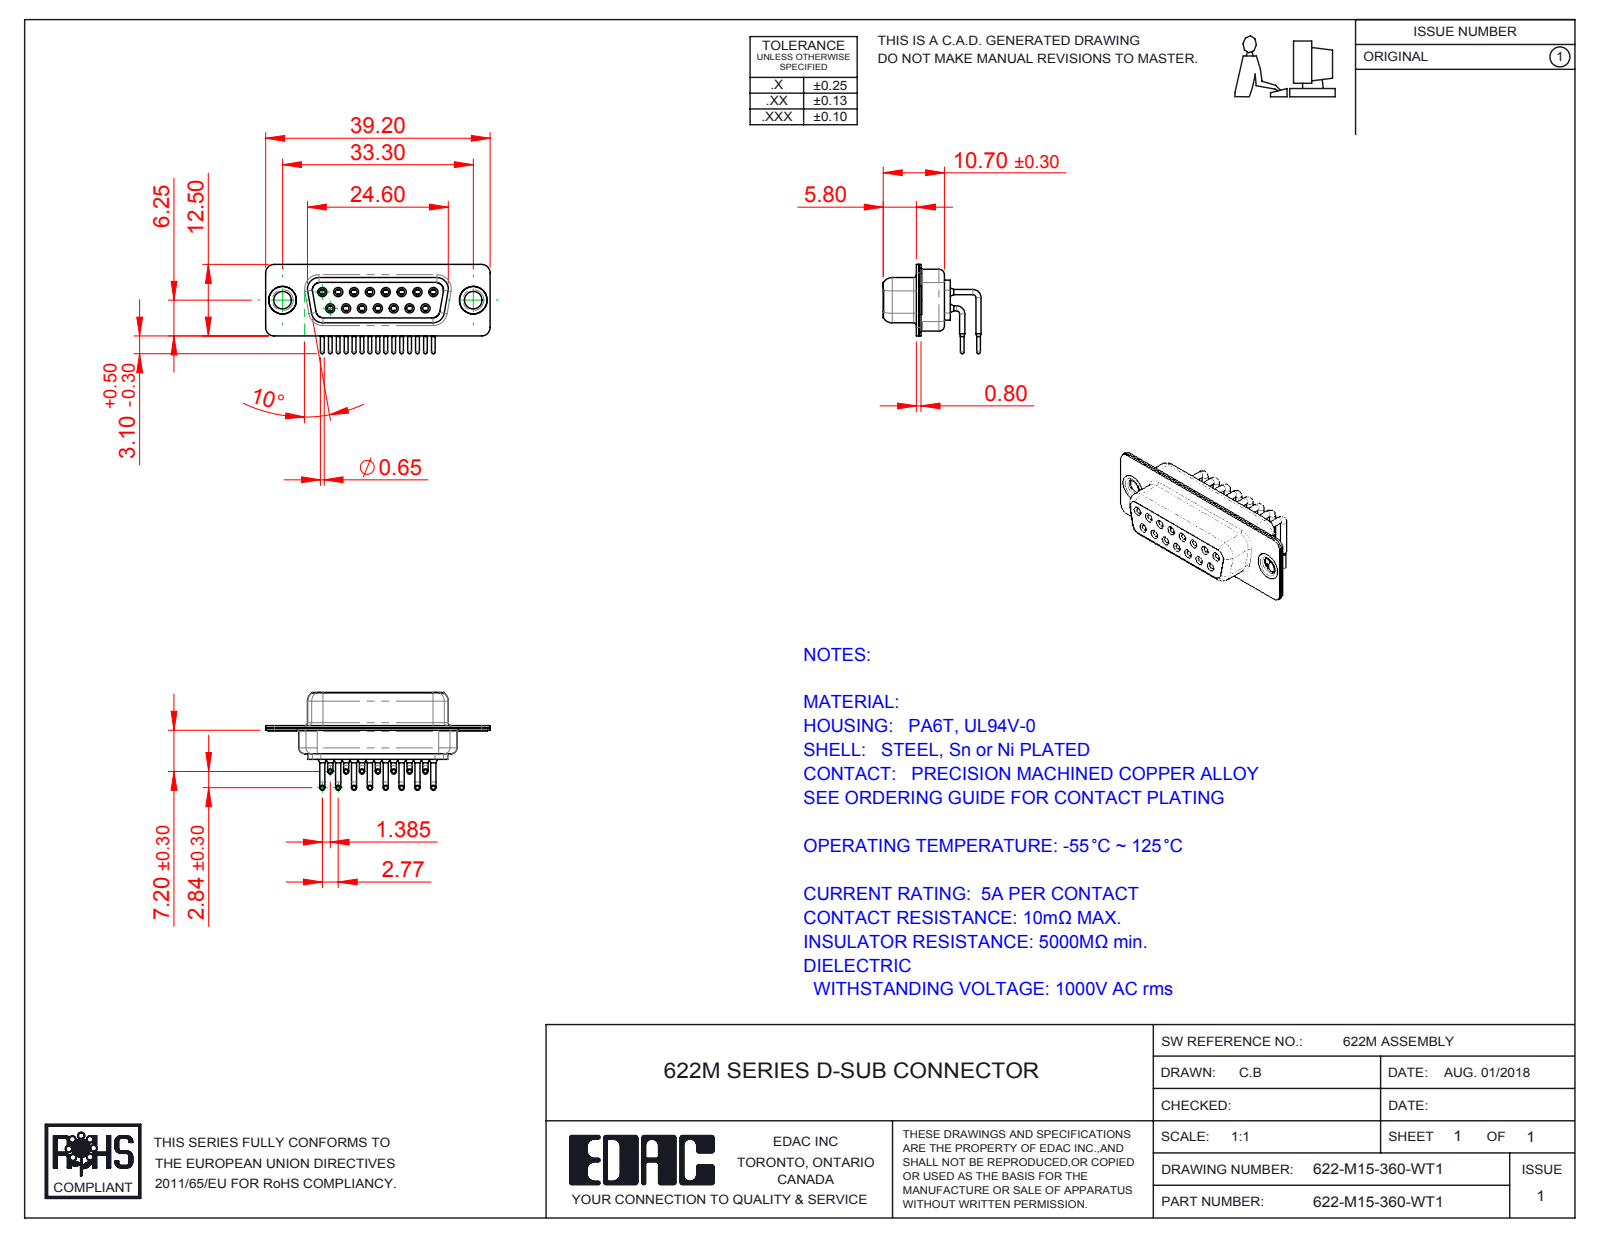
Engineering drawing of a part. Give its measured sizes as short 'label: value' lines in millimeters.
name: 622M Shell Rear_15 Contacts; 622-M15-360-WT1; 622M Shell Front_15 Contacts; 622M Housing_15 Contacts (+3 more)
written by: SolidWorks 2016 (CONFIG_CONTROL_DESIGN)
unit: mm
bodies: 20 solids, 1048 faces (292 planar, 466 cylindrical, 290 other)
size: 39.2 × 17.09 × 15.6
volume: 2 461 mm³; area: 6 268 mm²
holes: 15× ⌀1, 15× ⌀1.1, 15× ⌀1.7, 15× ⌀1.8, 15× ⌀2, 2× ⌀3.05, 2× ⌀4, 2× ⌀4.8
bosses: 30× ⌀0.9, 15× ⌀1.6, 15× ⌀1.5, 15× ⌀0.65, 2× ⌀5, 2× ⌀4.9, 2× ⌀3.55
rounds: 16× R1.5, 12× R2, 8× R1.35, 8× R1.6, 4× R0.25, 4× R0.5, 4× R0.6, 4× R0.65
face distances: 0.4, 1.45, 8.95, 6.2, 1.9, 8.5, 2.3, 0.45, 7.05, 0.85
hole spacings: 3.16, 2.77, 5.54, 8.31, 11.08, 5.03, 5.04, 7.48
